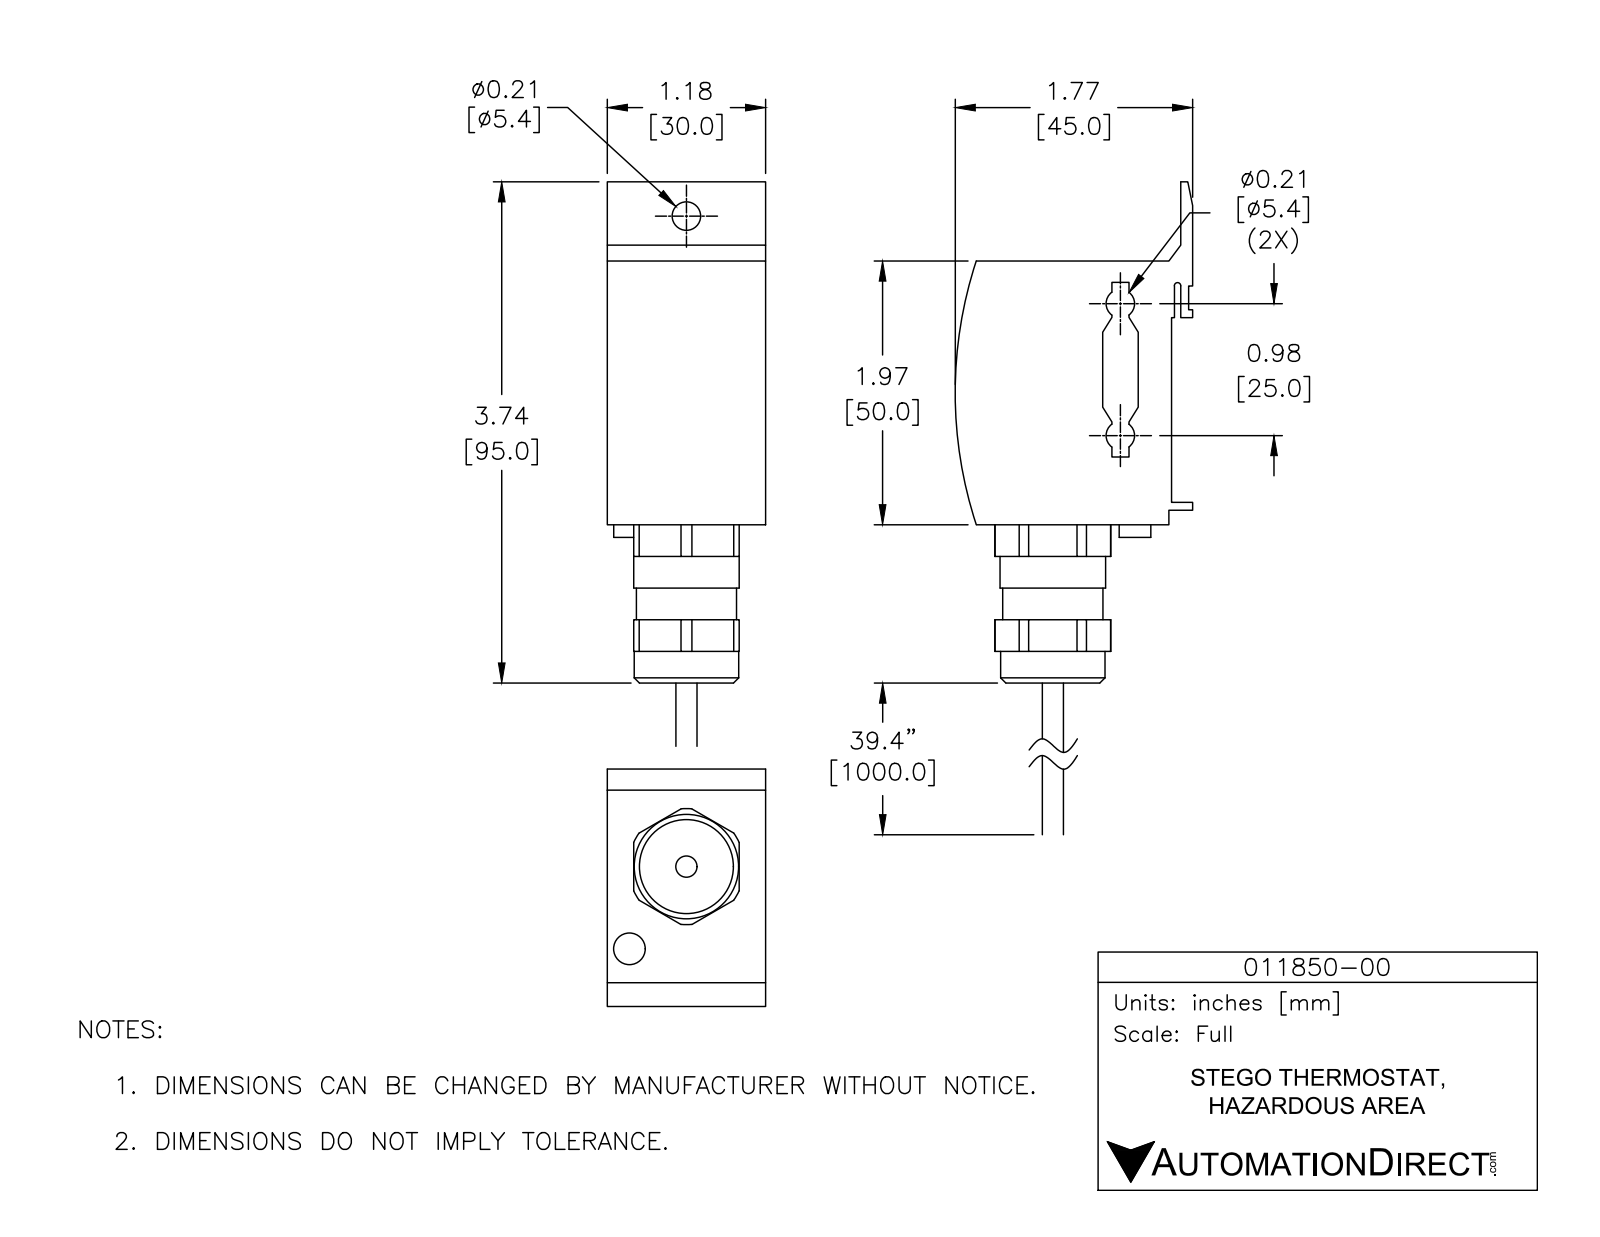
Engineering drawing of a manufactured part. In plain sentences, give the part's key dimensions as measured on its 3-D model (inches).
The part is named "PRODUCT_NAME_1". Its 3-D file was written by "ACIS (AUTOMOTIVE_DESIGN_CC2)". It is 1 solid with 98 faces: 62 planar, 34 cylindrical and 2 other. Overall it measures 4.213 by 1.772 by 1.181 inches. Its volume is 4.025 cubic inches and its surface area 23.63 square inches. Round holes: 1 of diameter 0.213. Round bosses or shafts: 1 of diameter 0.787, 1 of diameter 0.78, 1 of diameter 0.748, 1 of diameter 0.236, 1 of diameter 0.157. Partial cylindrical surfaces (rounded edges, fillets, slot ends): 2 of radius 0.106, 1 of radius 0.024, 1 of radius 0.433, 1 of radius 3.154. The main face-to-face distances are 1.181, 1.969, 0.069, 0.089, 0.514, 0.157, 0.406, 0.671, 0.317, 0.583.
